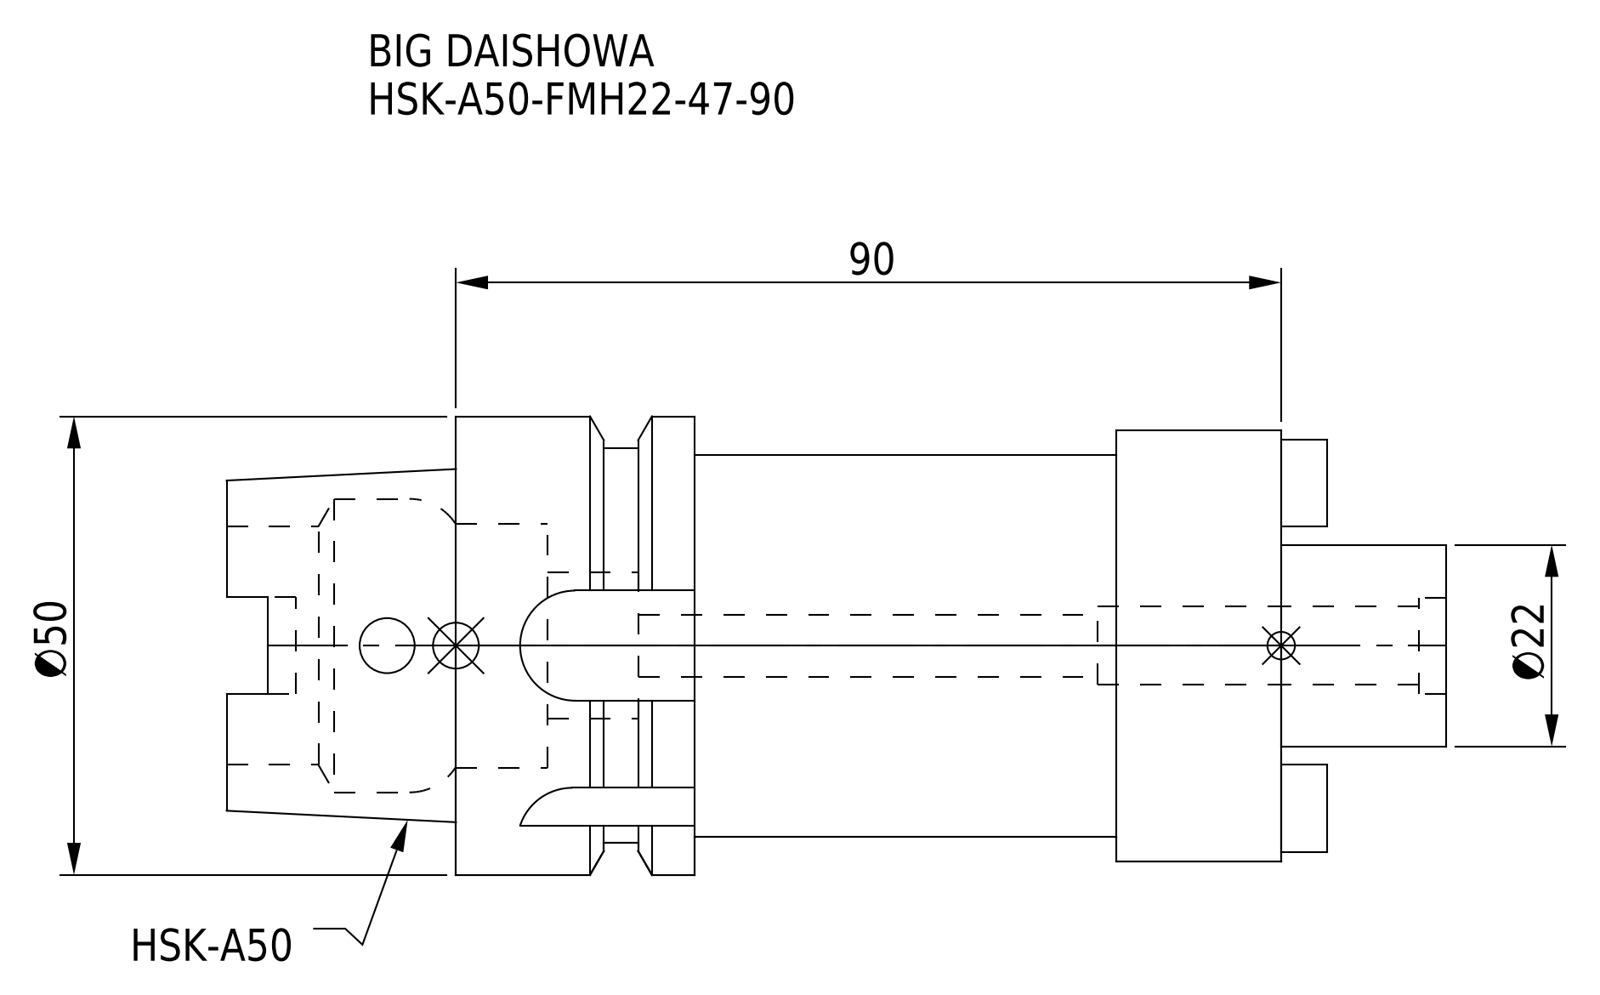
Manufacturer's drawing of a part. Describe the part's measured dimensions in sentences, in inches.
The part is named "HSK-A50-FMH22-47-90". Its 3-D file was written by "CREO PARAMETRIC BY PTC INC, 2016380 (AUTOMOTIVE_DESIGN)". It is 1 solid with 107 faces: 50 planar, 43 cylindrical and 14 other. Overall it measures 5.236 by 1.969 by 1.969 inches. Its volume is 8.952 cubic inches and its surface area 43.66 square inches. Round holes: 1 of diameter 0.236, 1 of diameter 0.268, 1 of diameter 0.335, 1 of diameter 0.413, 1 of diameter 0.63, 1 of diameter 1.024, 1 of diameter 1.047, 1 of diameter 1.26. Round bosses or shafts: 1 of diameter 1.969, 1 of diameter 1.85, 1 of diameter 1.693, 1 of diameter 1.638, 1 of diameter 0.866. Partial cylindrical surfaces (rounded edges, fillets, slot ends): 4 of radius 0.094, 4 of radius 0.236. The main face-to-face distances are 3.543, 1.024, 0.709, 2.52, 1.811, 2.835, 3.152, 2.443, 0.632, 0.392.
